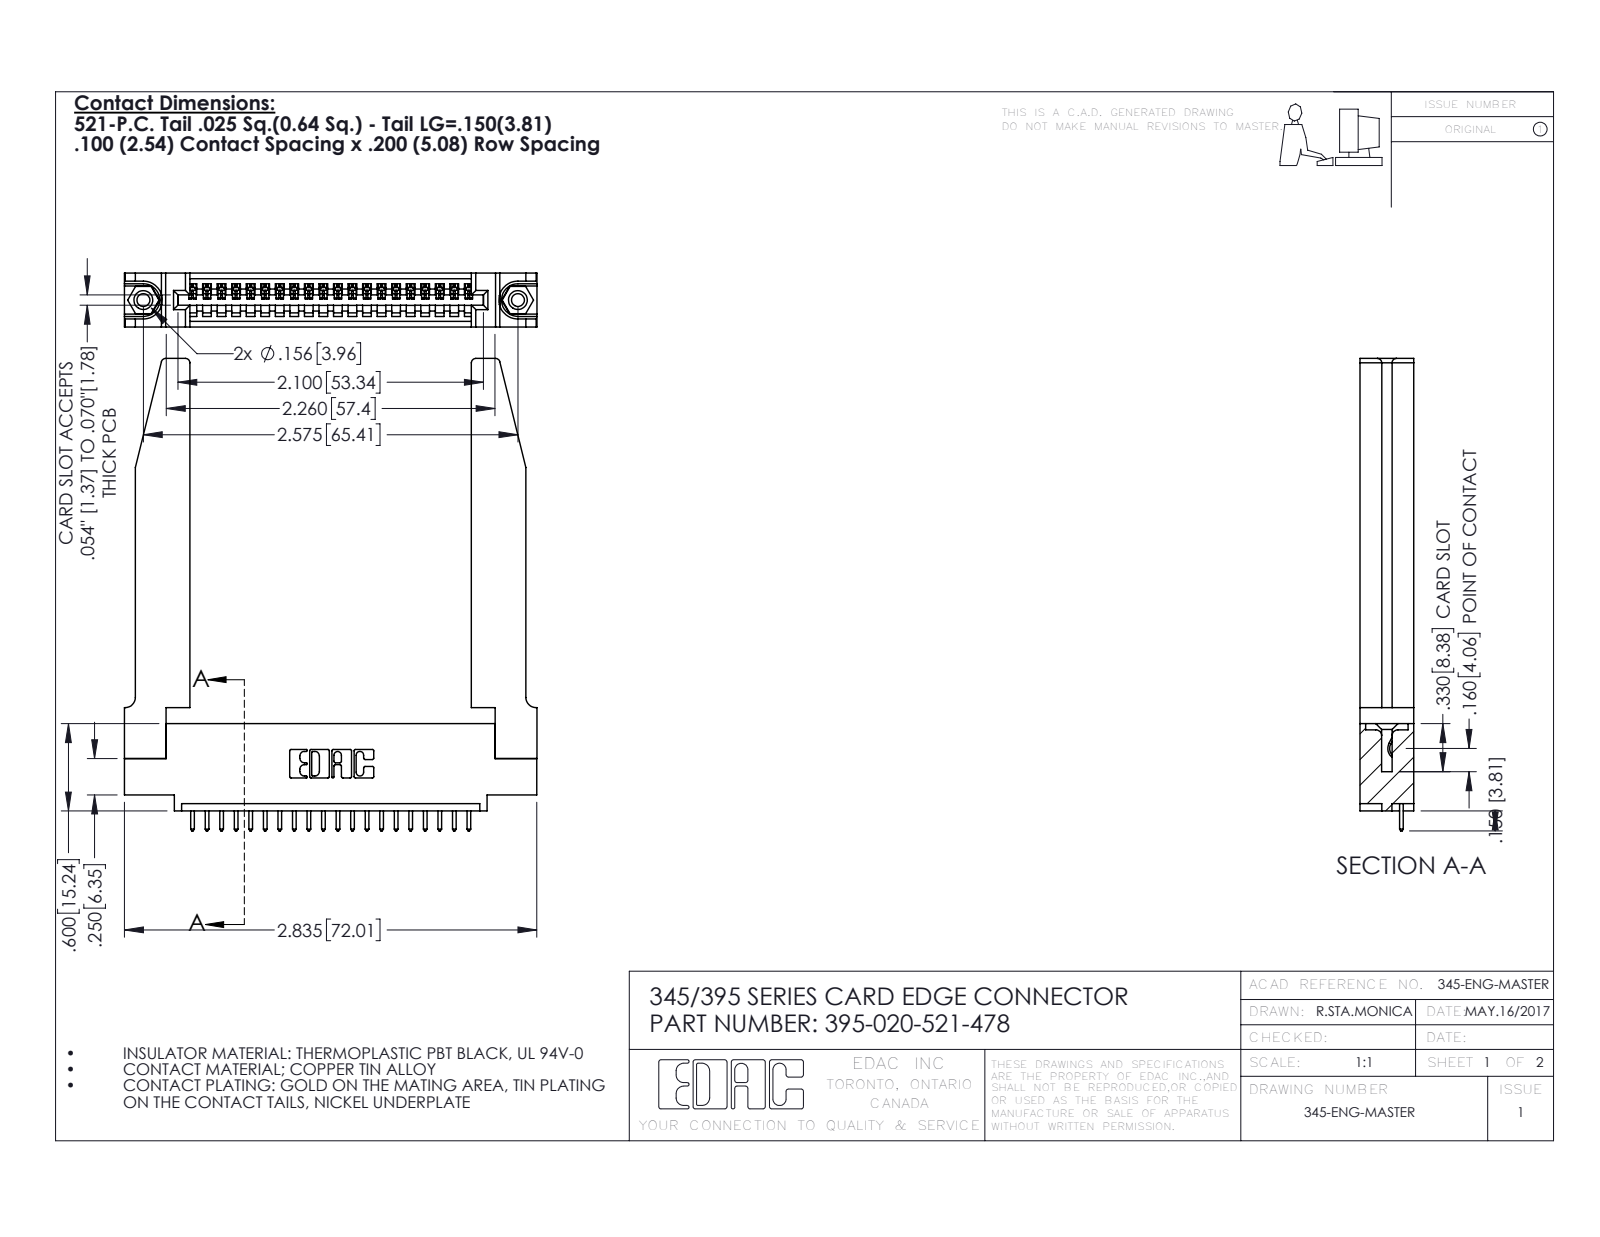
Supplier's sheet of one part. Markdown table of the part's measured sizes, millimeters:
| quantity | value |
| --- | --- |
| part name | 395-020-521-478; 345-220-078_345-220-078; 345-250-001_345-250-001-102; 345-292-001_345-293-121 (+1 more) |
| STEP written by | SolidWorks 2016 (CONFIG_CONTROL_DESIGN) |
| units | millimeters |
| bodies | 25 solids, 1524 faces (1026 planar, 446 cylindrical, 52 other) |
| overall size | 82.5 × 72 × 9.4 |
| volume | 14 300 mm³ |
| surface area | 15 080 mm² |
| round holes (diameter × count) | 2.3 × 2, 3.2 × 2, 4 × 2, 1.6 × 1 |
| round bosses / shafts (diameter × count) | 3.9 × 2 |
| partial cylindrical surfaces (radius × count) | 0.2 × 40, 0.3 × 40, 0.3 × 22, 0.8 × 8, 0.2 × 6, 0.8 × 6, 0.7 × 3, 0.8 × 2 |
| main face-to-face distances | 9.4, 1.8, 7.6, 5.1, 3.8, 3.8, 2.5, 6.9, 0.6, 5.6 |
| hole center spacings | 6.9, 59.5, 65.4 |
